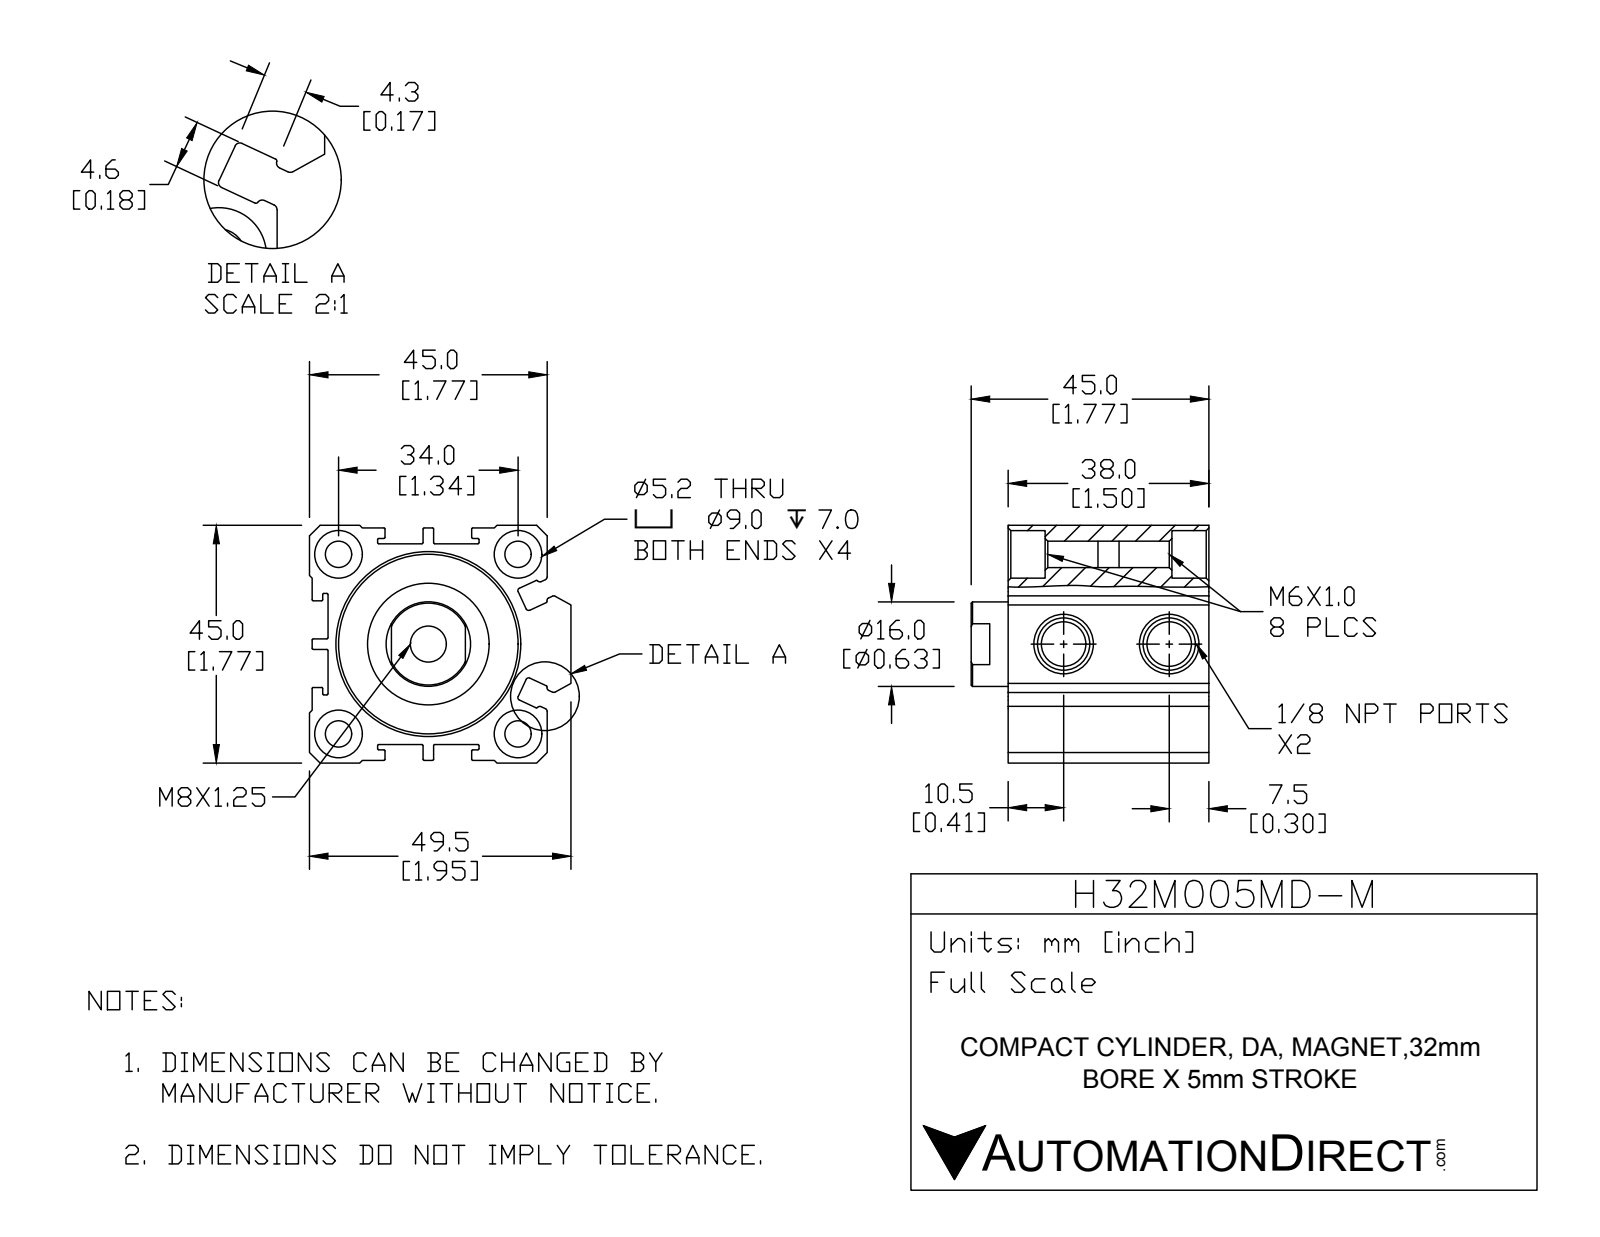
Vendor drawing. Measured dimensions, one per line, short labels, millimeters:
name: H32M005MD-M-PISTON; H32M005MD-M-BODY; H32M005MD-M
written by: SolidWorks 2015 (CONFIG_CONTROL_DESIGN)
unit: mm
bodies: 2 solids, 255 faces (99 planar, 103 cylindrical, 53 other)
size: 49.5 × 45 × 45
volume: 58 895 mm³; area: 26 365 mm²
holes: 4× ⌀5, 4× ⌀9, 2× ⌀8.43, 1× ⌀6.8, 1× ⌀16, 1× ⌀23, 1× ⌀28, 1× ⌀32, 1× ⌀34
bosses: 1× ⌀20
rounds: 40× R0.2, 12× R0.5
face distances: 3.5, 41.5, 3, 38, 45, 4.5, 44.5, 0.5, 23, 41
hole spacings: 24.04, 34, 48.08, 20
